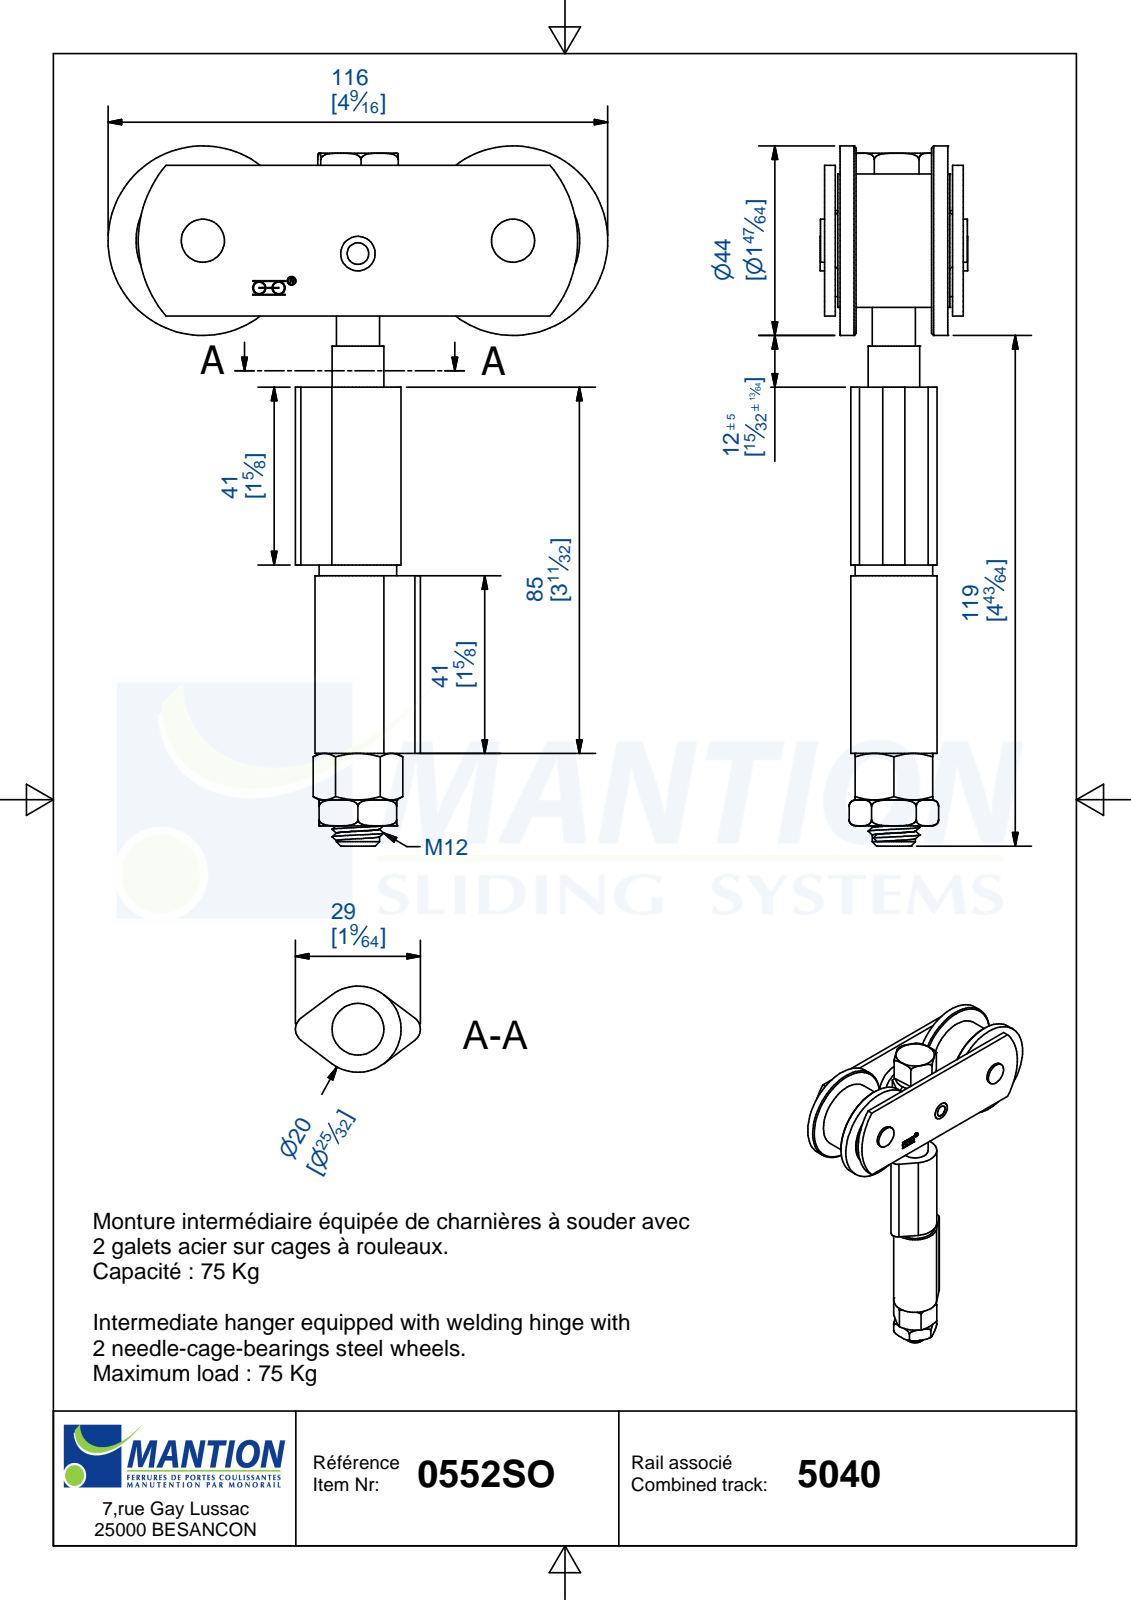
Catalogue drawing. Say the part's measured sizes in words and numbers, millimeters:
The part is named "552 SO; 14592; 15107; 11002 MONT (+8 more)". Its 3-D file was written by "Autodesk Inventor 2009 (AUTOMOTIVE_DESIGN)". It is 17 solids with 312 faces: 142 planar, 122 cylindrical and 48 other. Overall it measures 165 by 116 by 34.6 millimeters. Its volume is 98 391 cubic millimeters and its surface area 66 079 square millimeters. Round holes: 2 of diameter 14, 2 of diameter 24.15, 1 of diameter 8.1, 1 of diameter 10, 1 of diameter 12.1, 1 of diameter 12.2. Round bosses or shafts: 2 of diameter 44, 2 of diameter 31, 2 of diameter 23.8, 2 of diameter 17.5, 2 of diameter 10, 2 of diameter 7.7, 1 of diameter 20, 1 of diameter 18. Partial cylindrical surfaces (rounded edges, fillets, slot ends): 18 of radius 2.55, 2 of radius 3.2, 2 of radius 11.5, 2 of radius 27. The main face-to-face distances are 2.5, 29.7, 27.2, 26.1, 3.6, 28.6, 32.2, 1.1, 7.35, 24.85. The hole center spacings are 36.12, 72.
